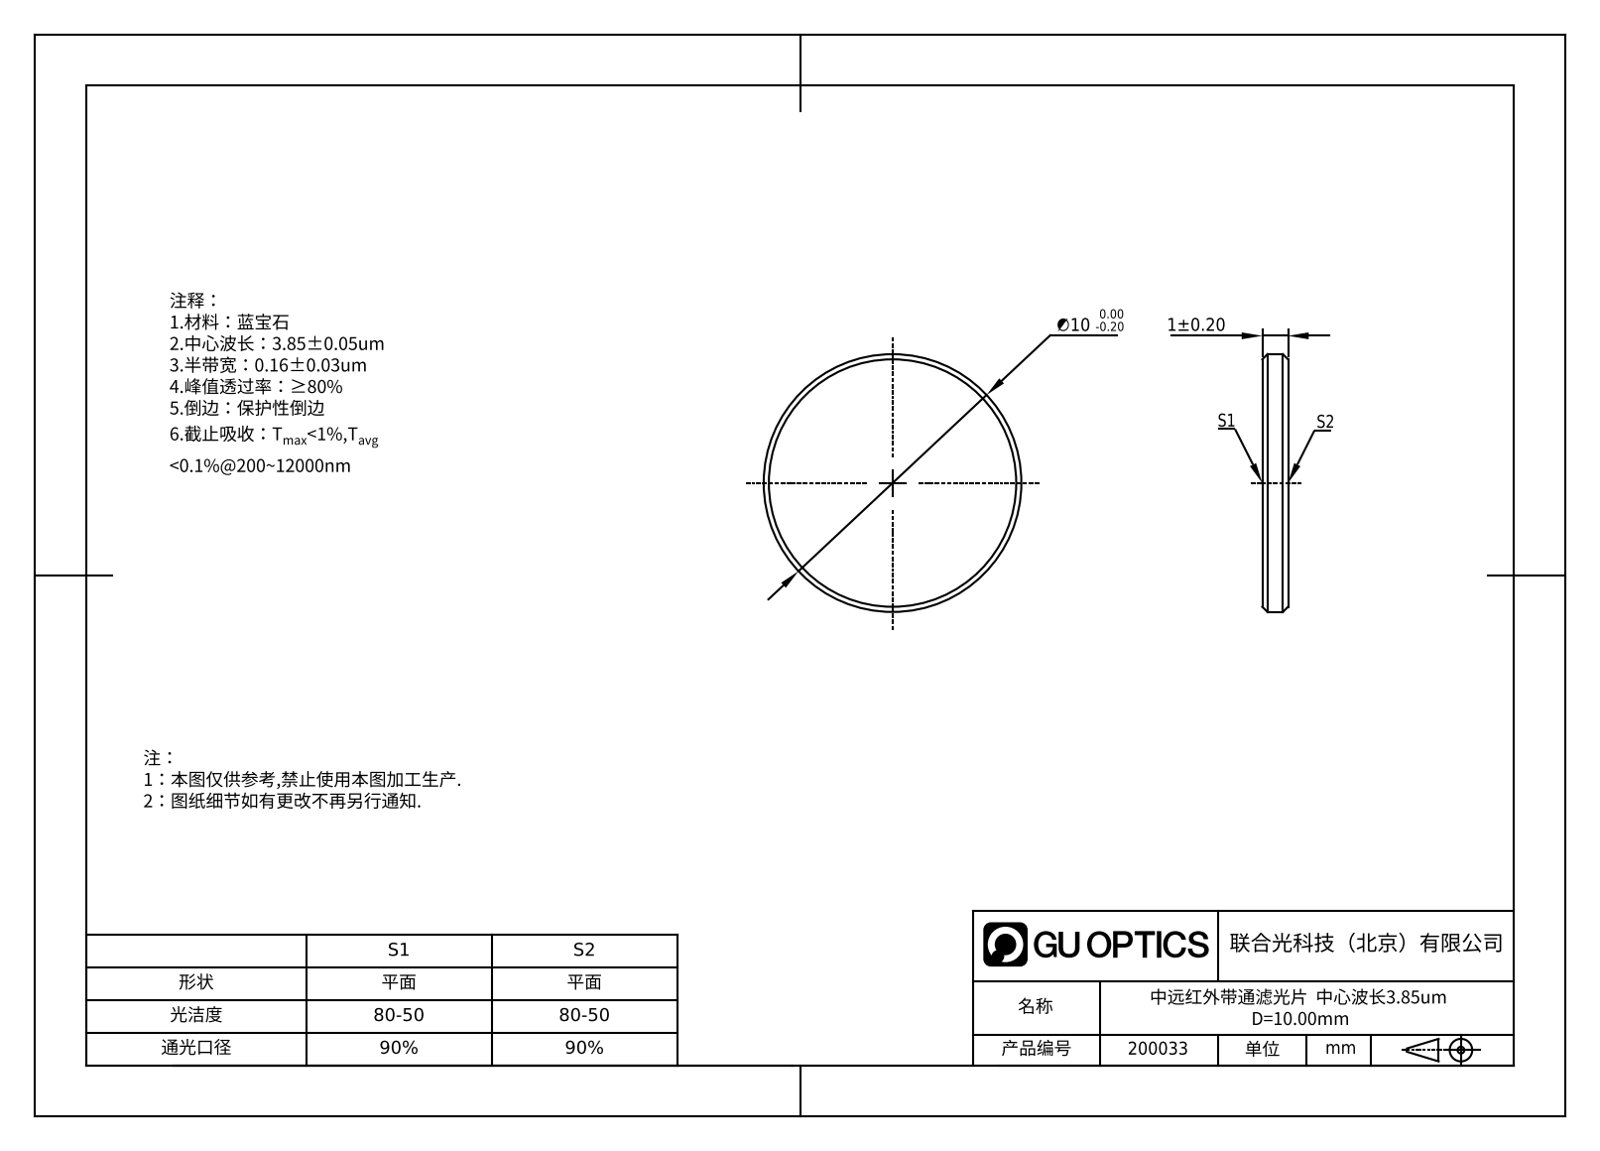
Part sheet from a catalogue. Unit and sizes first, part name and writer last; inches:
Units: inches
Overall size (bounding box): 0.394 × 0.394 × 0.039
Round bosses / shafts (diameter × count): ⌀0.394 ×1
Main face-to-face distances: 0.039
Volume: 0.005 in³ · Surface area: 0.281 in²
Bodies: 1 solid, 8 faces (2 planar, 2 cylindrical, 4 other)
Part name (STEP PRODUCT): GNIF-160-3850-D10
STEP written by: SolidWorks 2022 (AUTOMOTIVE_DESIGN)
